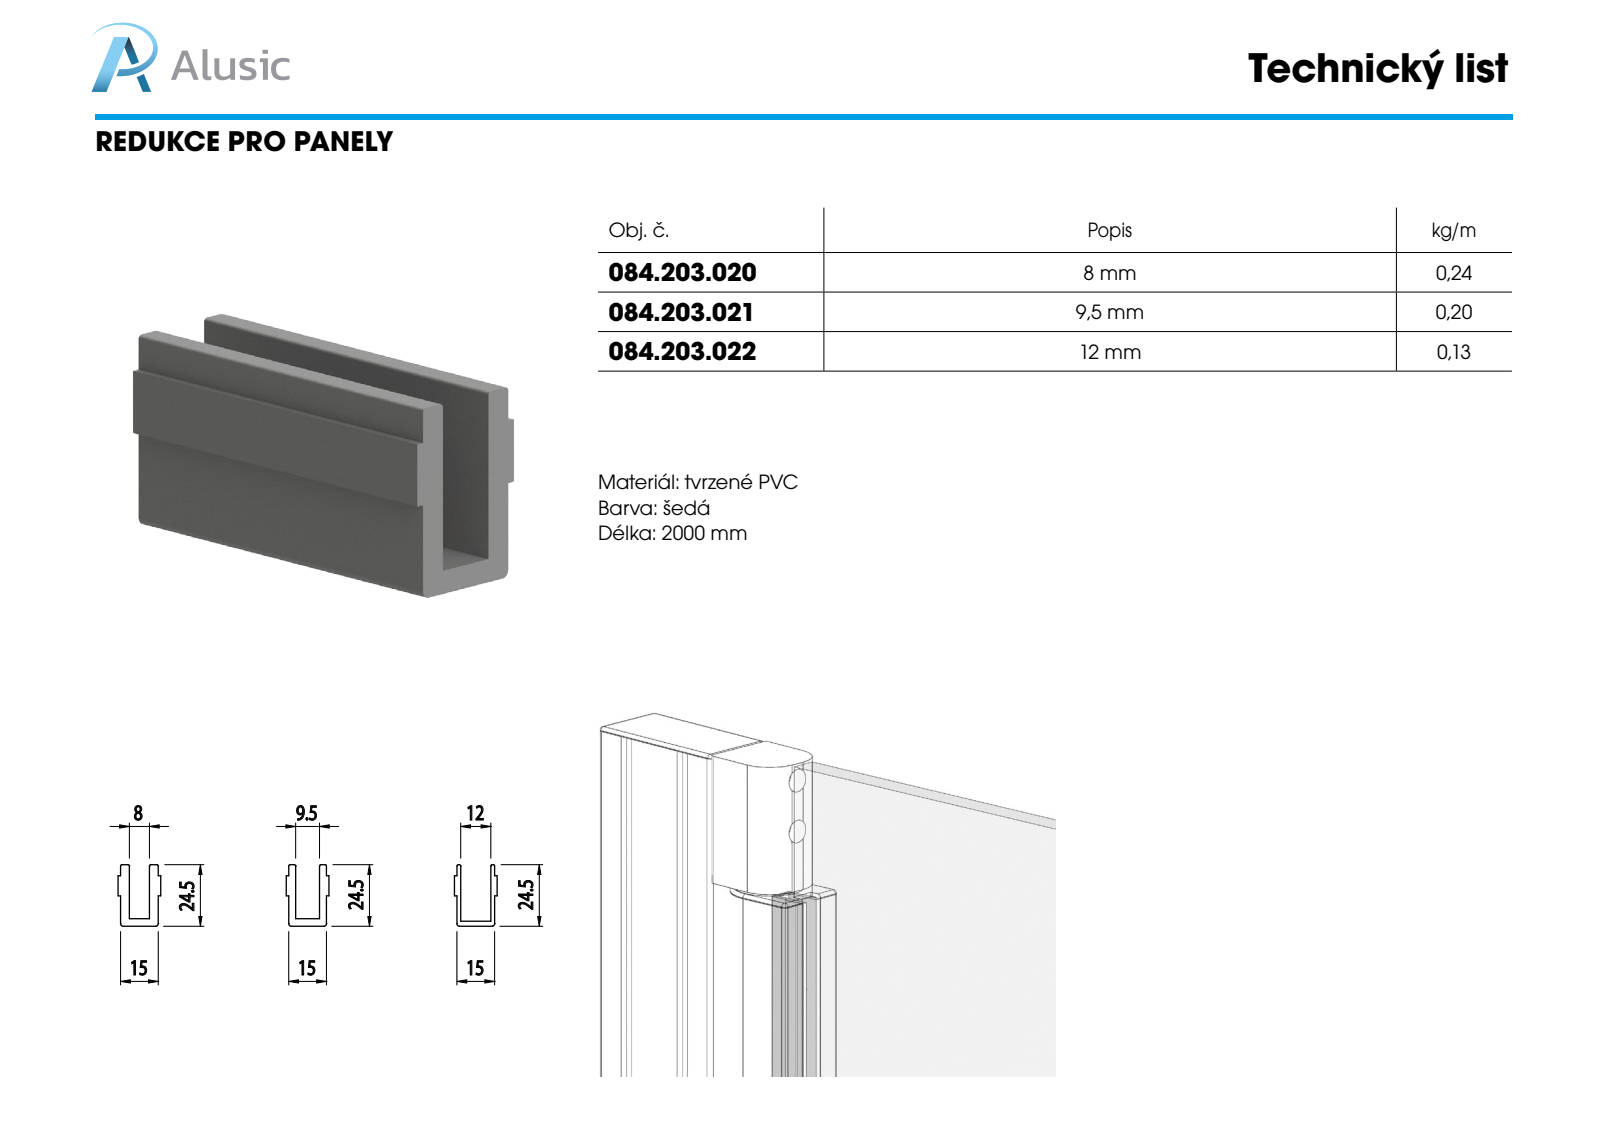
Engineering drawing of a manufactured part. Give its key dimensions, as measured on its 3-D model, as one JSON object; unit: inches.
{"part_name": "084.203.021", "step_written_by": "SolidWorks 2012 (CONFIG_CONTROL_DESIGN)", "units": "inches", "bodies": {"solids": 1, "faces": 24, "planar": 18, "cylindrical": 6, "other": 0}, "overall_size": [3.937, 0.965, 0.669], "volume_in3": 1.09, "surface_area_in2": 19.82, "partial_cylinders_radius": [[0.02, 4], [0.039, 2]], "face_to_face_distances": [0.108, 0.482, 0.374, 0.039, 0.148, 0.522, 0.63, 0.591, 0.118, 0.669]}
